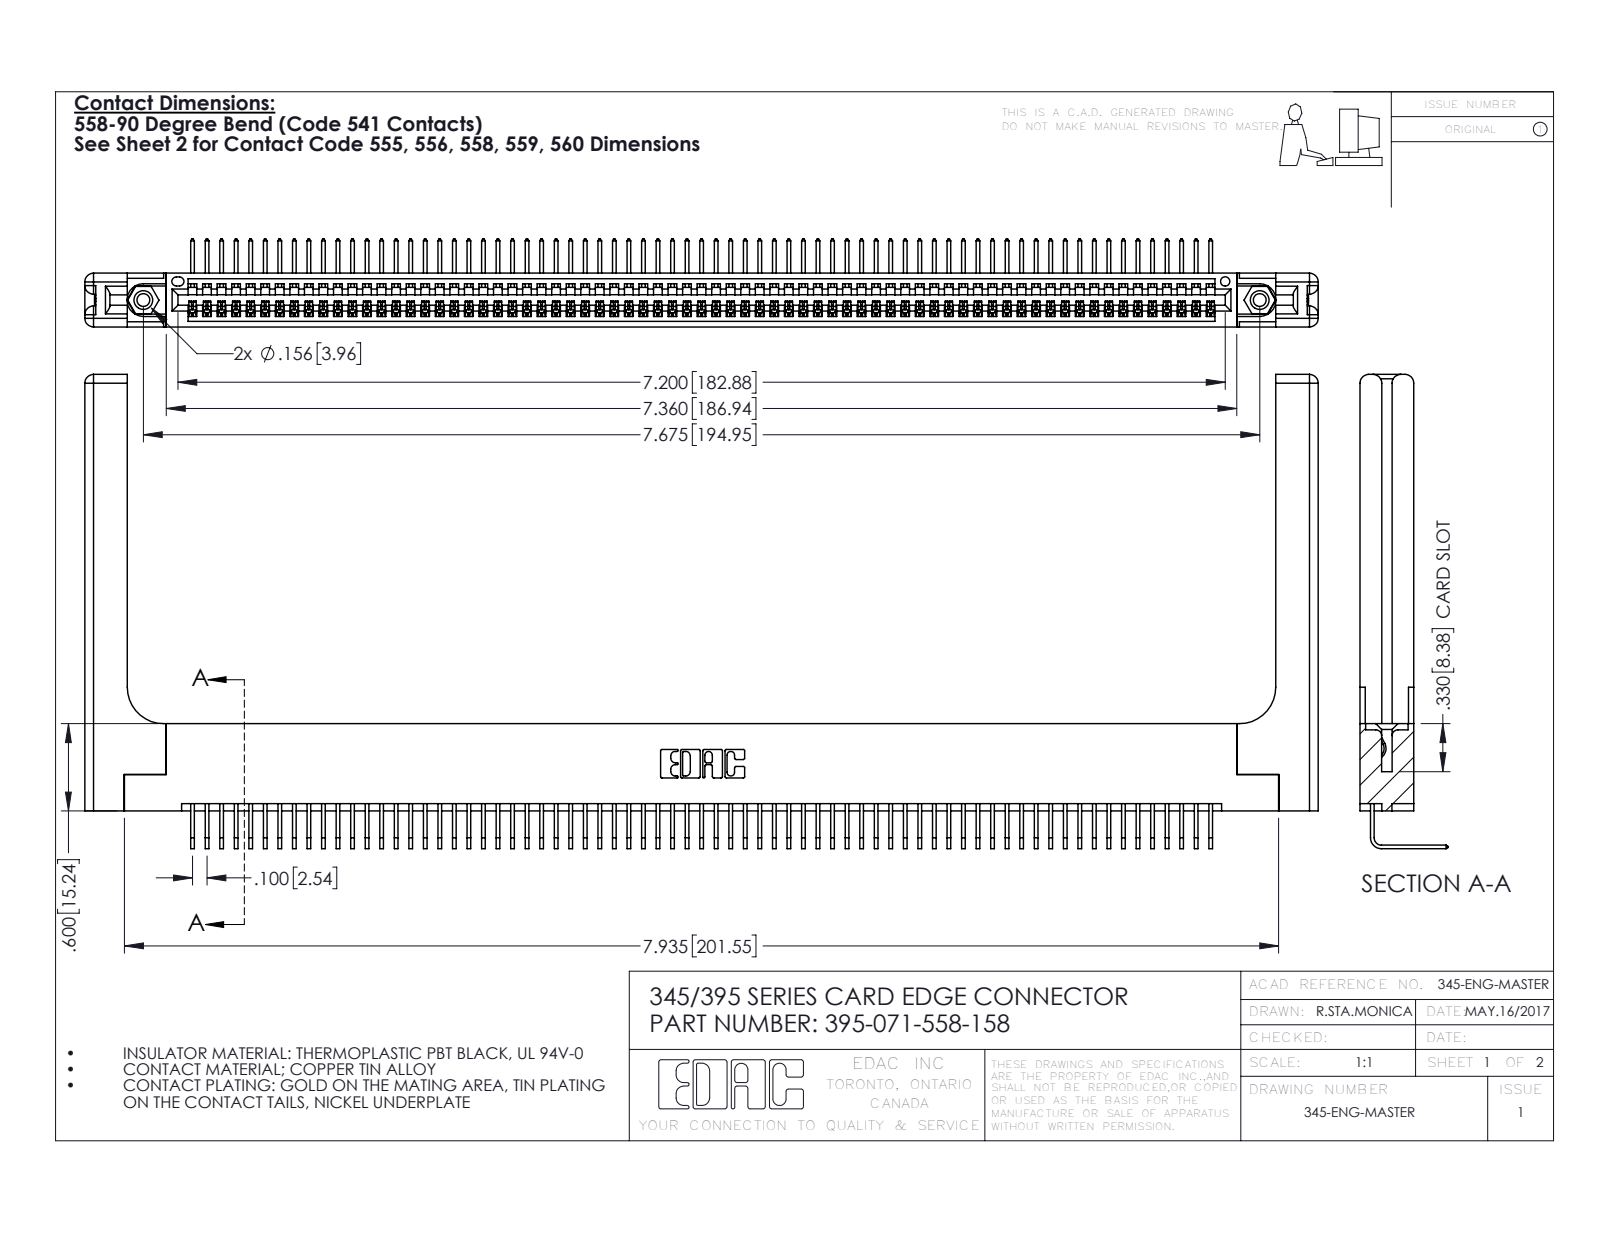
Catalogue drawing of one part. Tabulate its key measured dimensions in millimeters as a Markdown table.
| quantity | value |
| --- | --- |
| part name | 345-220-058_345-220-058; 395-071-558-158; 345-250-001_345-250-001-102; 345 Part_Flush Mounting Lugs - 0.156 Dia-TH (+1 more) |
| STEP written by | SolidWorks 2016 (CONFIG_CONTROL_DESIGN) |
| units | millimeters |
| bodies | 76 solids, 4642 faces (3210 planar, 1372 cylindrical, 60 other) |
| overall size | 215.4 × 82.8 × 15.4 |
| volume | 29 430 mm³ |
| surface area | 34 900 mm² |
| round holes (diameter × count) | 2.3 × 2, 3.2 × 2, 4 × 2, 1.6 × 1 |
| round bosses / shafts (diameter × count) | 3.9 × 2 |
| partial cylindrical surfaces (radius × count) | 0.2 × 142, 0.3 × 22, 1.5 × 16, 0.2 × 6, 0.8 × 6, 0.7 × 3, 0.8 × 2, 0.8 × 2 |
| main face-to-face distances | 1.8, 7.6, 9.4, 5.1, 2.5, 6.9, 0.6, 5.7, 3.8, 3.8 |
| hole center spacings | 6.9, 189, 194.9 |
